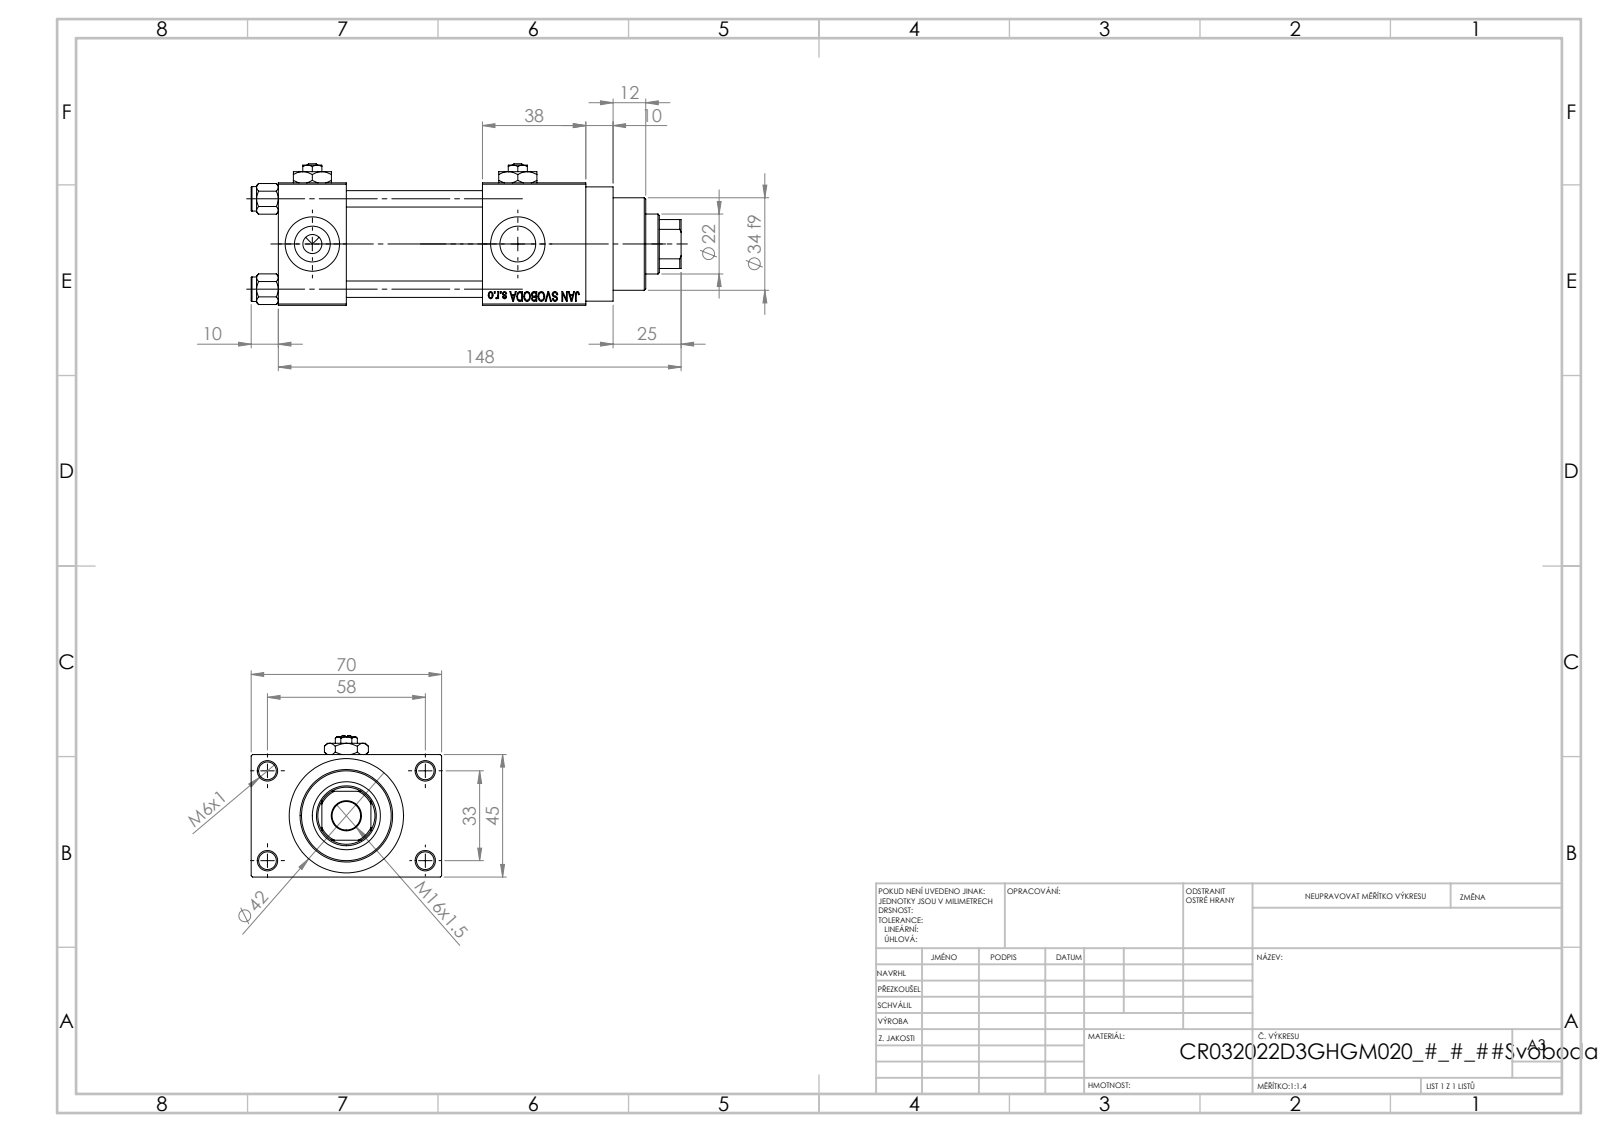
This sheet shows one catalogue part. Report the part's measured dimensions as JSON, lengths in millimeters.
{"part_name": "V215CR_D_TYCINKA; V215_VC_A; V215CR_D_Body; V215CR_VCP_D (+2 more)", "step_written_by": "SolidWorks 2019 (CONFIG_CONTROL_DESIGN)", "units": "millimeters", "bodies": {"solids": 13, "faces": 1201, "planar": 542, "cylindrical": 99, "other": 560}, "overall_size": [158, 70, 52], "volume_mm3": 241745, "surface_area_mm2": 81712, "round_holes": [[6, 4], [6.5, 4], [13.16, 4], [20, 4], [7, 3], [10.5, 1], [22, 1], [24, 1], [25, 1], [32, 1], [33, 1]], "round_bosses_or_shafts": [[9, 4], [42, 1], [38, 1], [34, 1]], "partial_cylinders_radius": [[10.5, 1]], "face_to_face_distances": [45, 25, 50, 12.5, 75, 57.5, 88, 38, 113, 70], "hole_center_spacings": [12.4, 23.48, 33.2, 33.37, 35.35, 45.6, 56.35, 33]}
